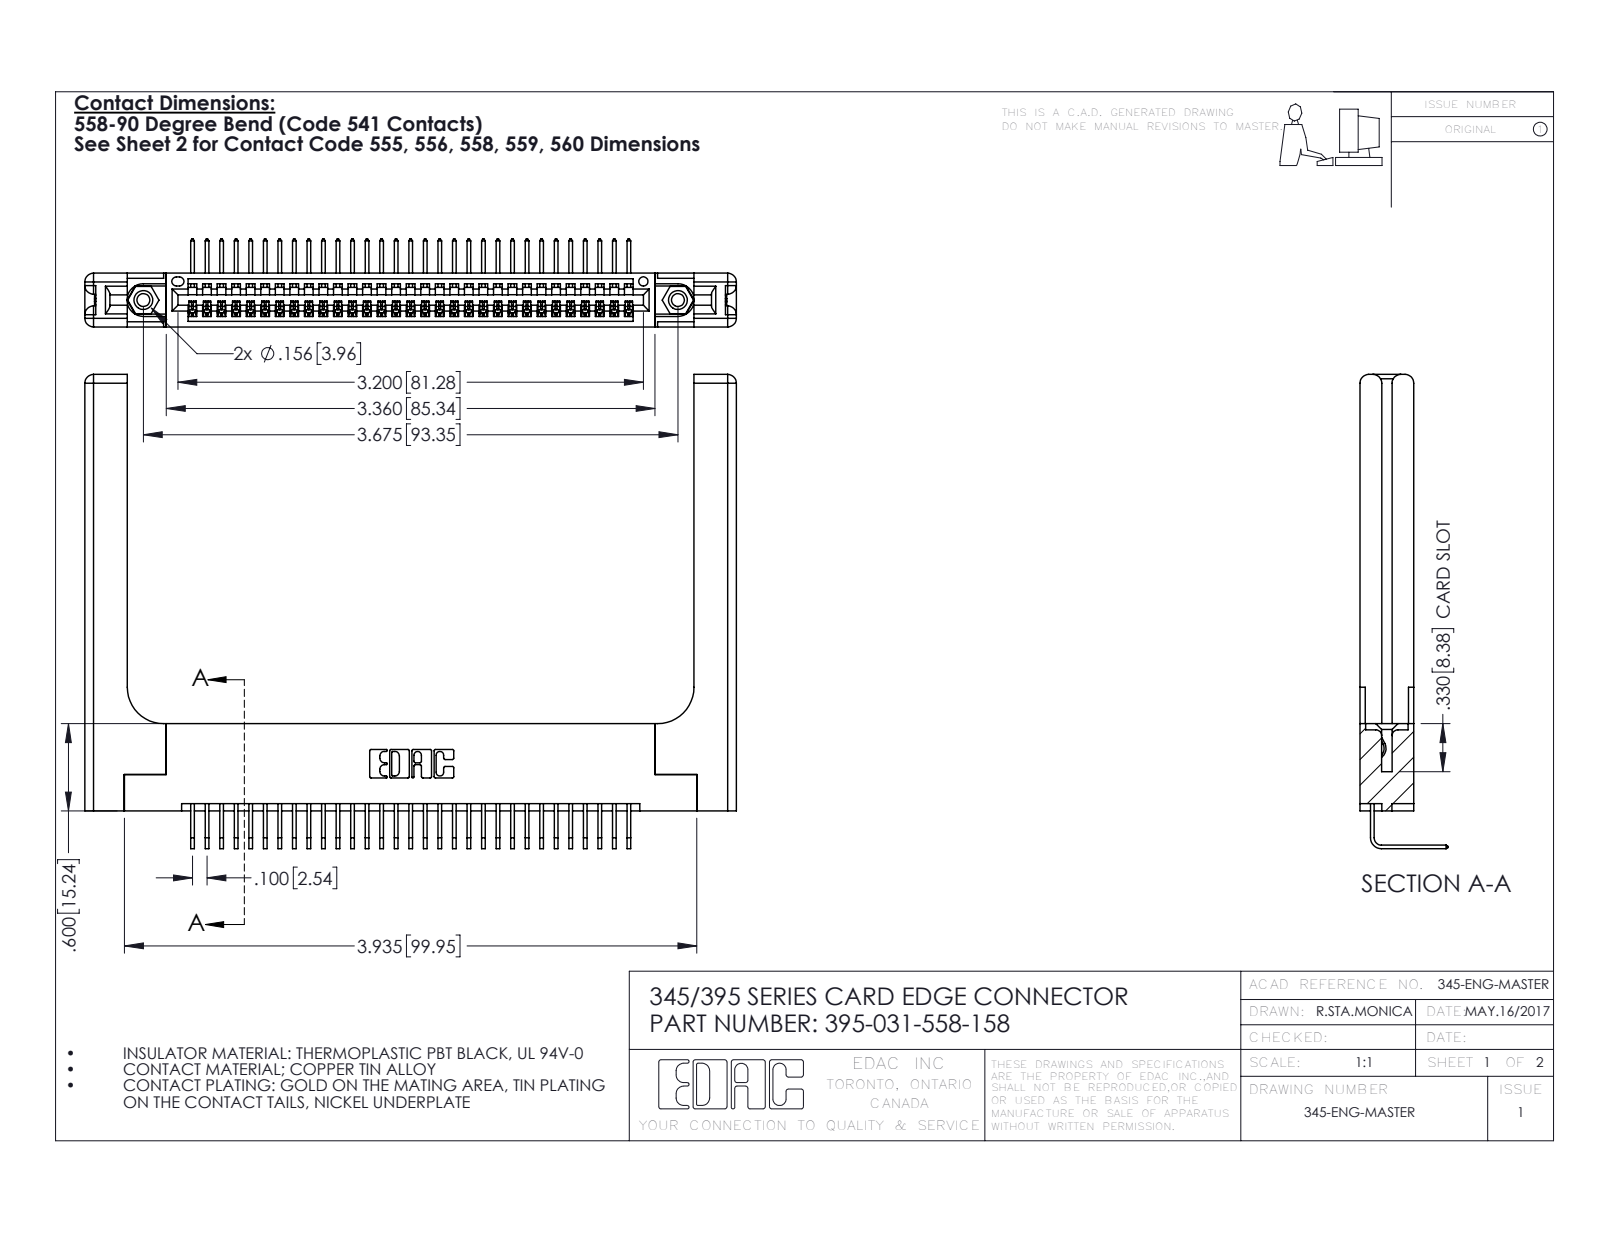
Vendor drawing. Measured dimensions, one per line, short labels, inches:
name: 395-031-558-158; 345 Part_Flush Mounting Lugs - 0.156 Dia-TH; 345-220-058_345-220-058; 345-292-001_558 Tail - 2 (+1 more)
written by: SolidWorks 2016 (CONFIG_CONTROL_DESIGN)
unit: in
bodies: 36 solids, 2242 faces (1530 planar, 652 cylindrical, 60 other)
size: 4.479 × 3.259 × 0.605
volume: 1.179 in³; area: 31.22 in²
holes: 2× ⌀0.089, 2× ⌀0.125, 2× ⌀0.156, 1× ⌀0.064
bosses: 2× ⌀0.155
rounds: 62× R0.006, 22× R0.01, 16× R0.06, 6× R0.007, 6× R0.031, 3× R0.026, 2× R0.03, 2× R0.031
face distances: 0.37, 0.072, 0.298, 0.2, 0.098, 0.272, 0.025, 0.148, 0.15, 0.077
hole spacings: 0.27, 3.44, 3.675
